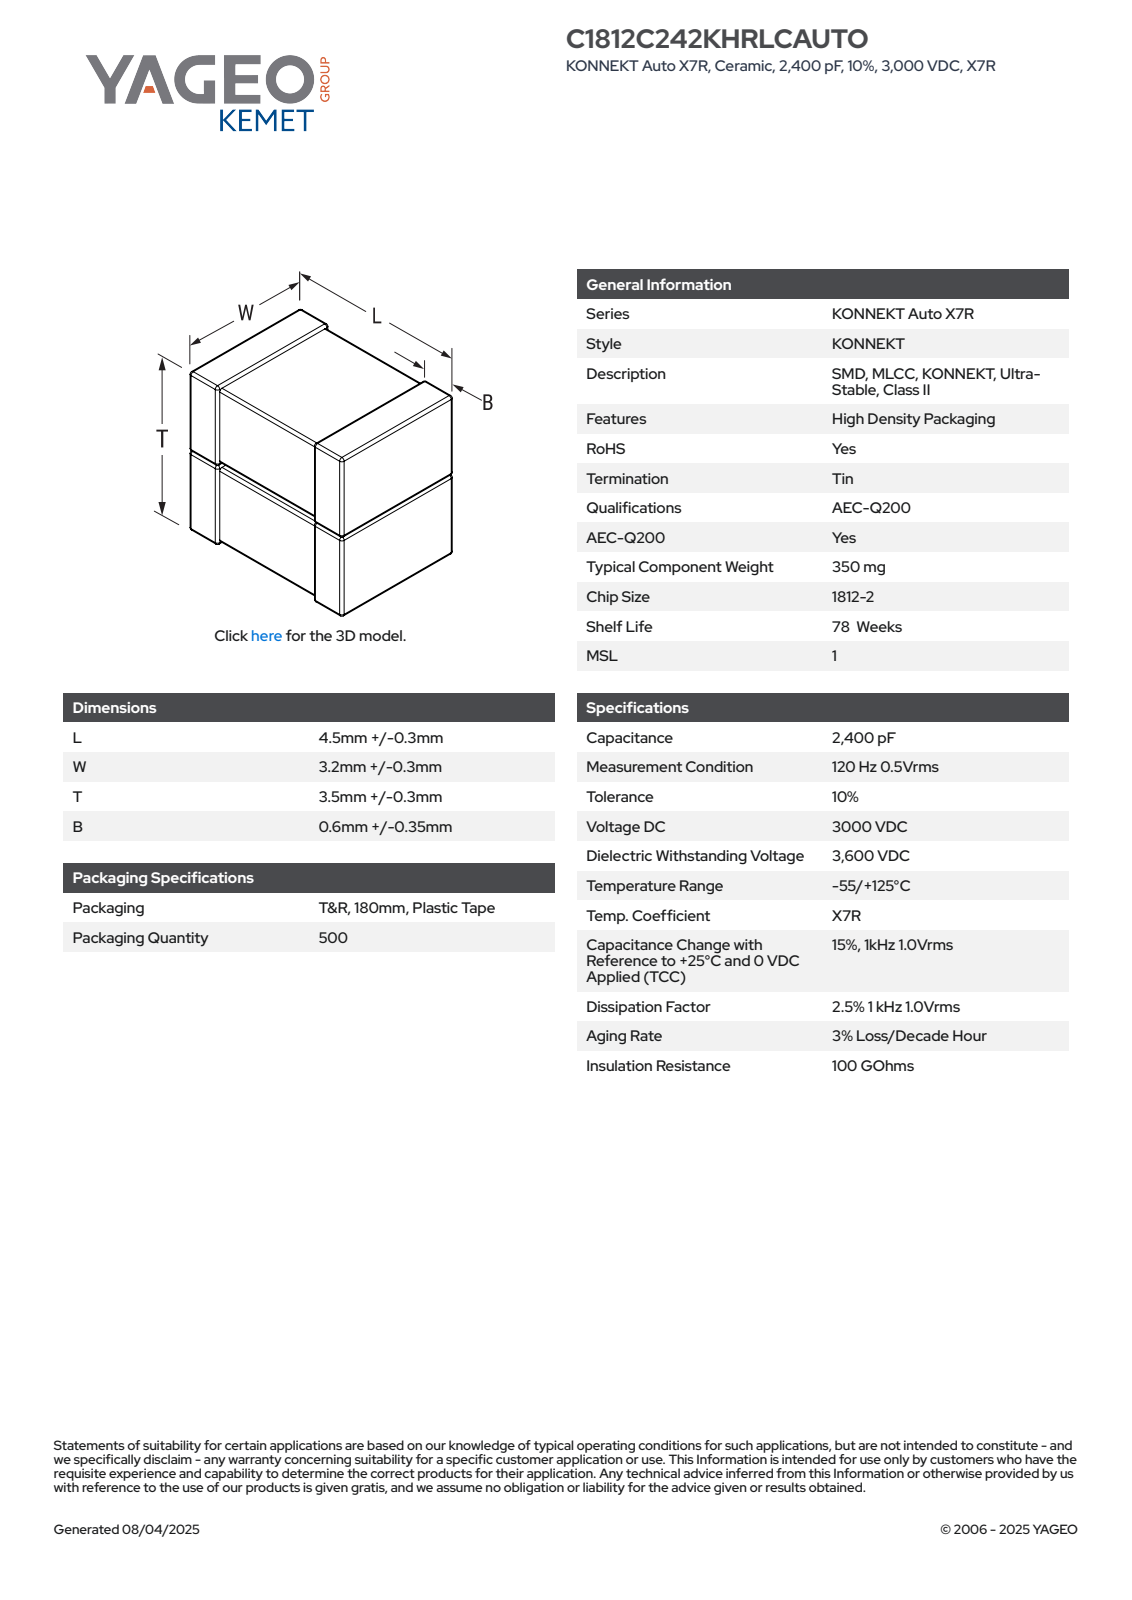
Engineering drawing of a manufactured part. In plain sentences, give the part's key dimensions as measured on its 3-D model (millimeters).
The part is named "CCSS_K2T_1812-2_L4.8W3.5B0.95T3.8". Its 3-D file was written by "SolidWorks 2020 (AUTOMOTIVE_DESIGN)". It is 4 solids with 189 faces: 81 planar, 76 cylindrical and 32 other. Overall it measures 4.8 by 3.8 by 3.5 millimeters. Its volume is 59 cubic millimeters and its surface area 116 square millimeters. The main face-to-face distances are 1.76, 1.9, 4.8, 3.43, 1.83, 1.97, 3.73, 3.36, 3.66, 3.5.
